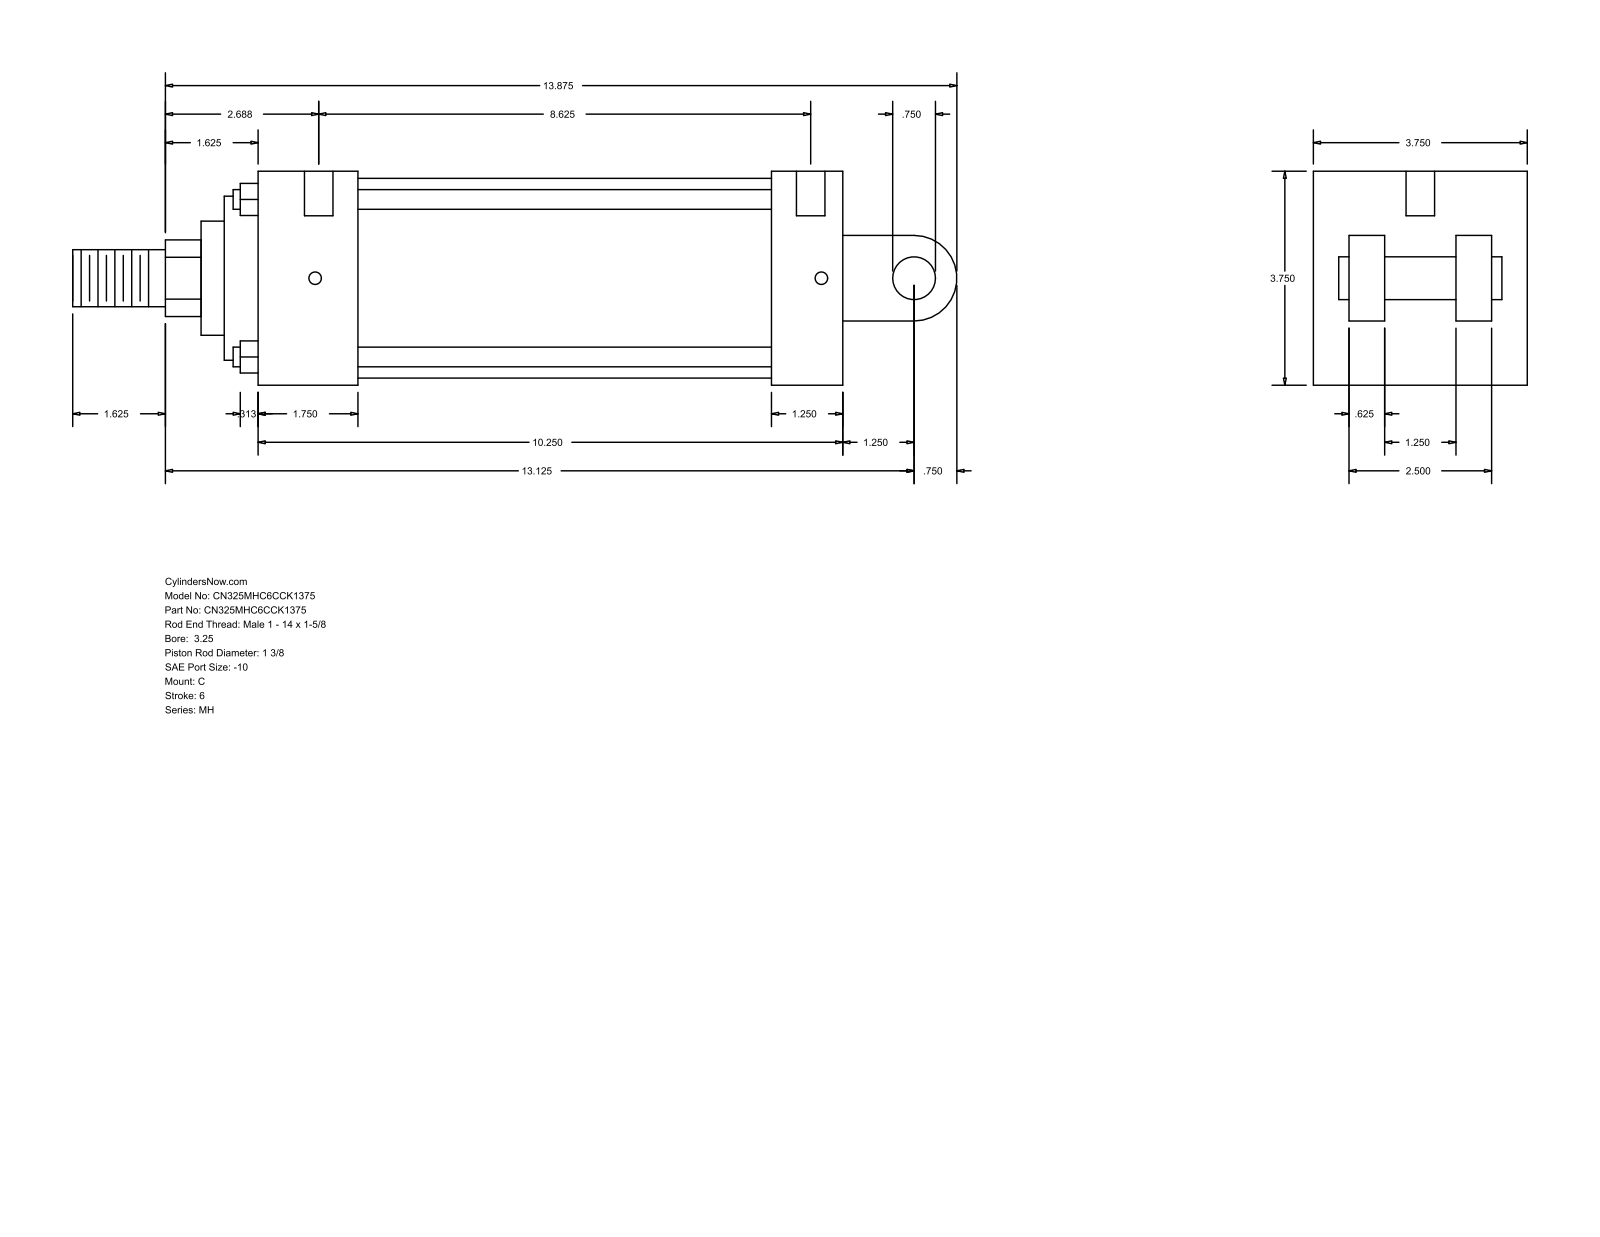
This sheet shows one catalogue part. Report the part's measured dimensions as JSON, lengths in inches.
{"part_name": "MH_C__0325_1.375", "step_written_by": "GSSL Pune (CONFIG_CONTROL_DESIGN)", "units": "inches", "bodies": {"solids": 0, "faces": 101, "planar": 71, "cylindrical": 30, "other": 0}, "overall_size": [15.5, 3.75, 3.75], "round_holes": [[0.219, 4], [0.5, 2]], "round_bosses_or_shafts": [[0.345, 4], [3.5, 1], [2.875, 1], [2, 1], [1.375, 1], [1, 1], [0.75, 1]], "partial_cylinders_radius": [[0.672, 1], [0.75, 1]], "face_to_face_distances": [3.75, 0.625, 1.25, 2.5, 10.25, 3.125, 1.875, 1.75, 9, 7.25], "hole_center_spacings": [8.875, 0.063, 0.187, 8.625, 8.688, 8.813]}
